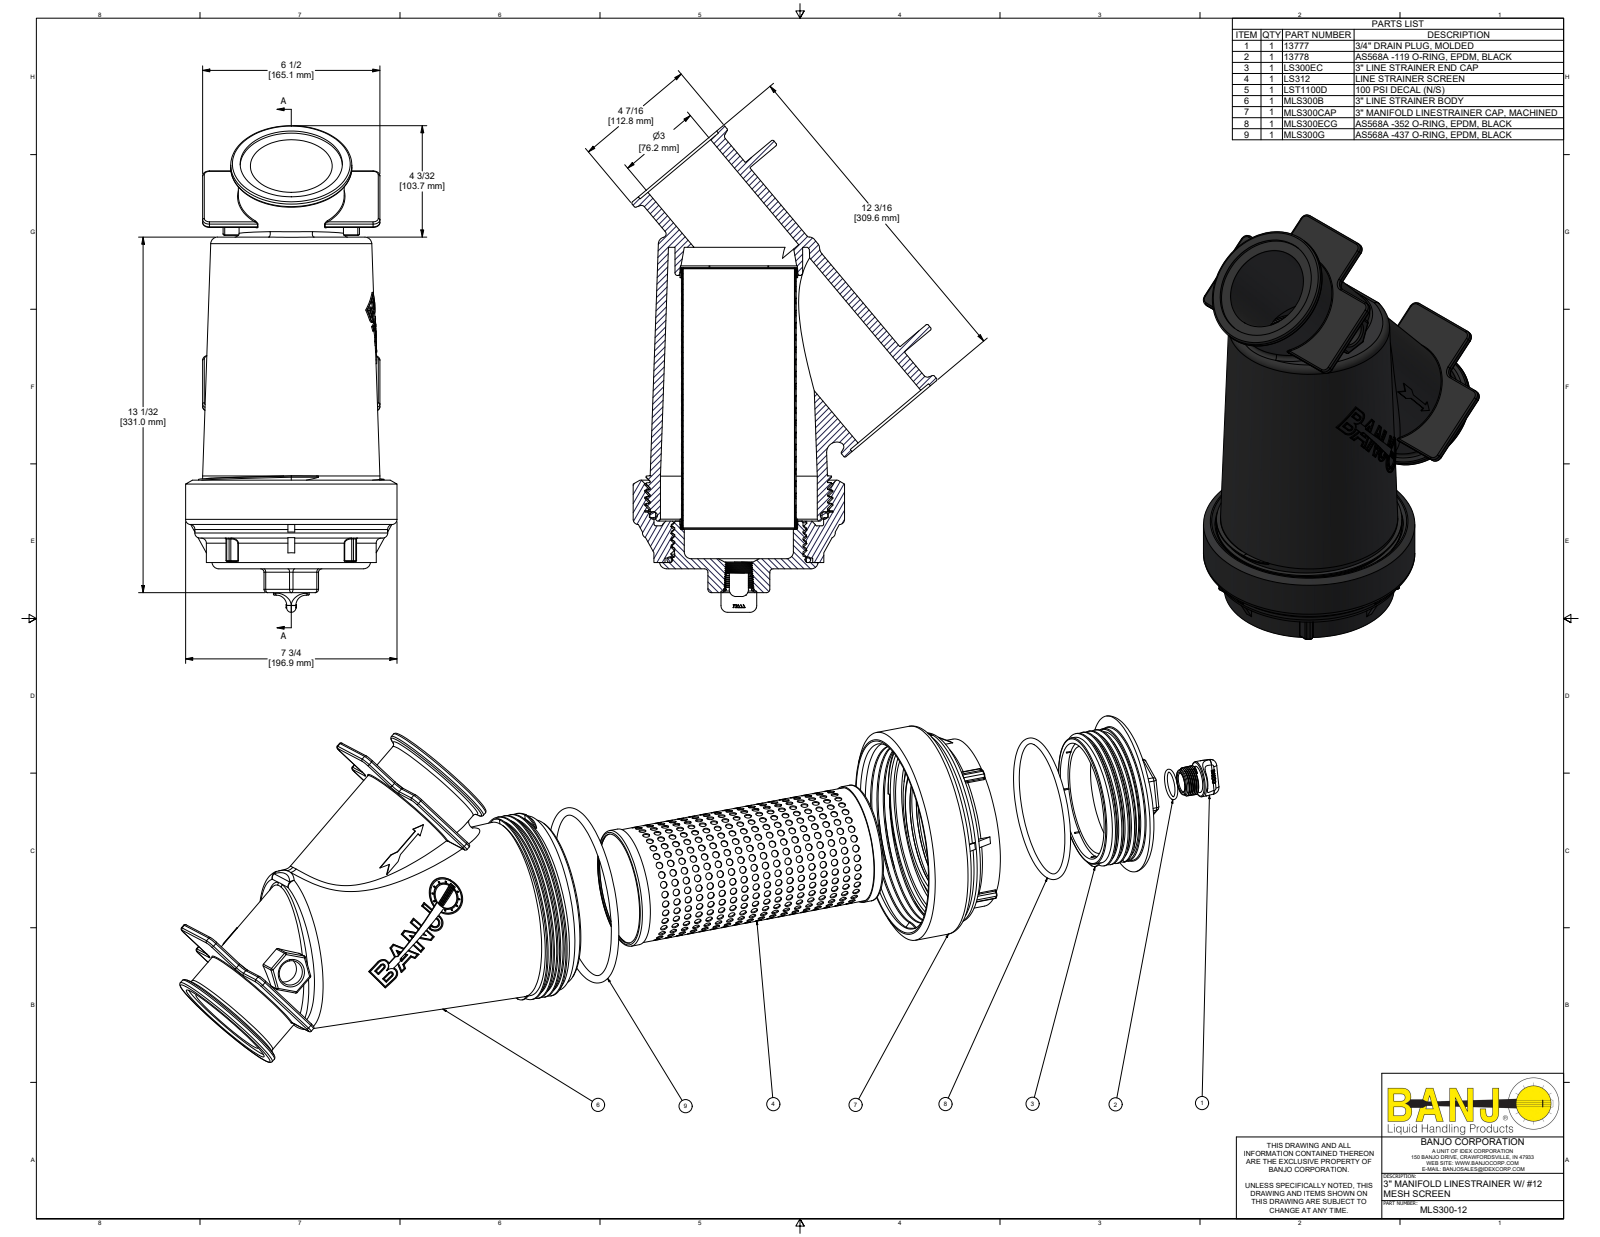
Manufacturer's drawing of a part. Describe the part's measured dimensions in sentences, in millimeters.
The part is named "MLS300-12; MLS300B; LS300EC; LS300ECX (+7 more)". Its 3-D file was written by "Autodesk Inventor 2022 (AUTOMOTIVE_DESIGN)". It is 11 solids with 1888 faces: 504 planar, 936 cylindrical and 448 other. Overall it measures 453 by 284.1 by 196.9 millimeters. Its volume is 3 115 000 cubic millimeters and its surface area 974 800 square millimeters. Round holes: 594 of diameter 6.4, 2 of diameter 95.3, 1 of diameter 17.8, 1 of diameter 20.8, 1 of diameter 23.1, 1 of diameter 29.3, 1 of diameter 76.2, 1 of diameter 101.6, 1 of diameter 103.2, 1 of diameter 103.6, 1 of diameter 105, 1 of diameter 107.5. Round bosses or shafts: 2 of diameter 112.8, 2 of diameter 98.6, 1 of diameter 196.9, 1 of diameter 179.6, 1 of diameter 172.7, 1 of diameter 165.1, 1 of diameter 158.2, 1 of diameter 154.9. Partial cylindrical surfaces (rounded edges, fillets, slot ends): 46 of radius 1.5, 28 of radius 0.8, 18 of radius 3.2, 17 of radius 6.4, 8 of radius 0.5, 8 of radius 2.3, 6 of radius 0.4, 2 of radius 1.8. The main face-to-face distances are 6.4, 223.9, 5.8, 217.6, 230.3, 43.5, 37.1, 261, 267.4, 9.4. The hole center spacings are 11.3, 22.7, 34, 45.4, 56.7, 68, 79.4, 90.7.
